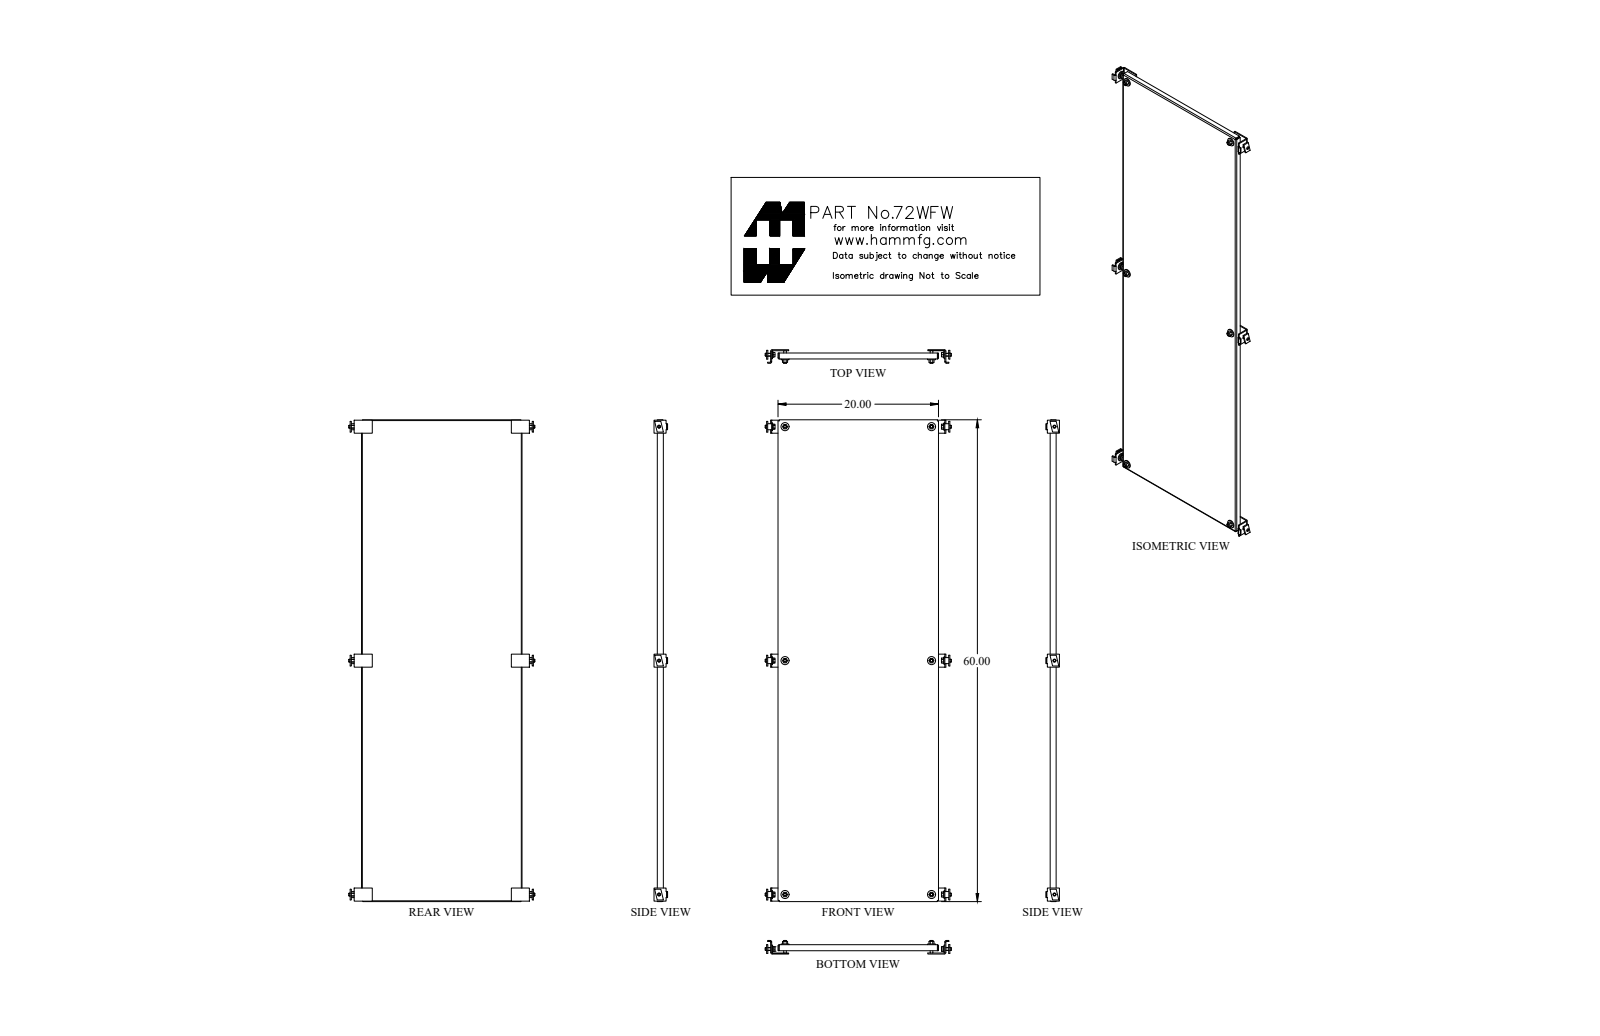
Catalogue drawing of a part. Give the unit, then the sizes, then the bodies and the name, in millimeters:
Units: millimetres
Overall size (bounding box): 1524 × 508 × 19.1
Round holes (diameter × count): ⌀14.3 ×6
Partial cylindrical surfaces — rounded edges, fillets, slot ends (radius × count): R1.2 ×4, R3.6 ×4
Main face-to-face distances: 2.4, 505.6, 503.2, 508, 1521.6, 19.1, 16.6, 1524, 1519.2, 3.6
Hole centre spacings: 739.8, 873, 463.6, 1479.6, 1550.4
Volume: 2 017 000 mm³ · Surface area: 1 683 000 mm²
Bodies: 1 solid, 42 faces (22 planar, 20 cylindrical, 0 other)
Part name (STEP PRODUCT): 72WFW_Default
STEP written by: SolidWorks 2018 (CONFIG_CONTROL_DESIGN)
